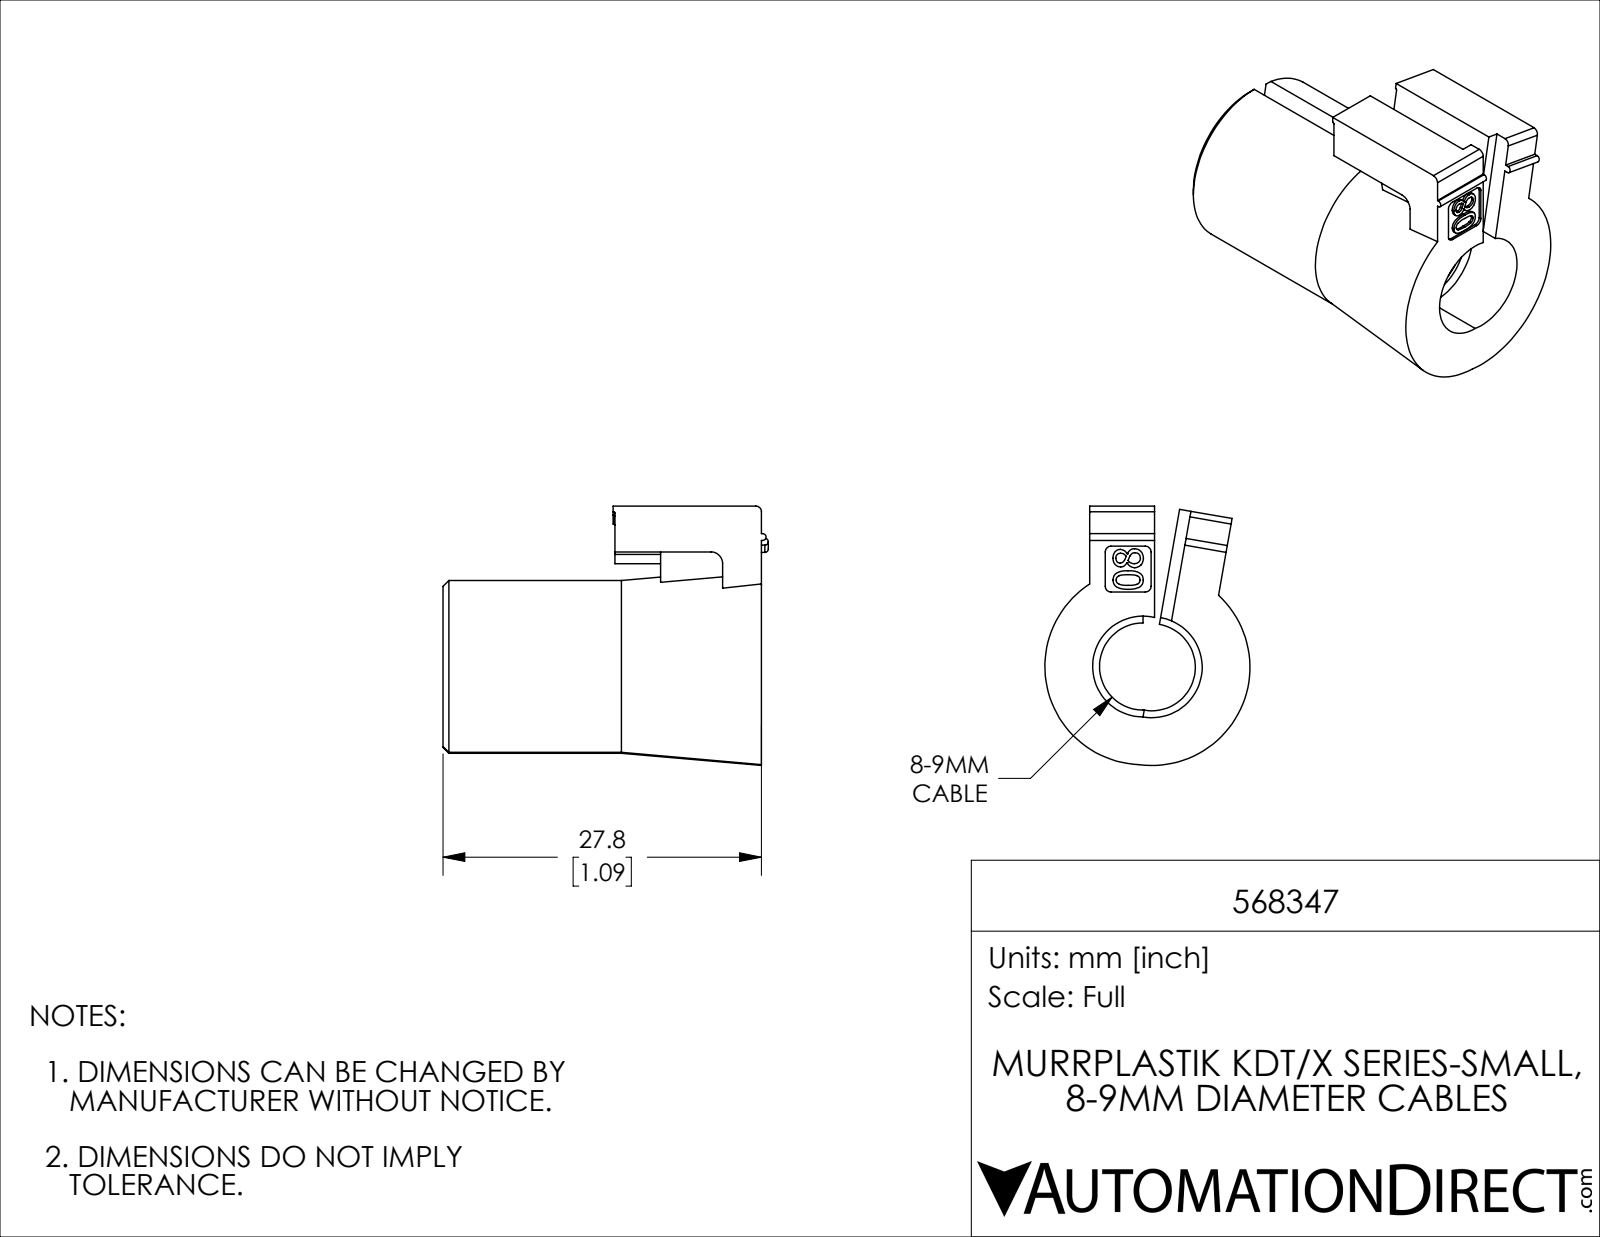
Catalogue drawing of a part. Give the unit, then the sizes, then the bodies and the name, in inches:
Units: inches
Overall size (bounding box): 1.118 × 0.891 × 0.705
Partial cylindrical surfaces — rounded edges, fillets, slot ends (radius × count): R0.02 ×6, R0.004 ×2, R0.012 ×2, R0.039 ×2, R0.15 ×2, R0.173 ×2, R0.295 ×2
Main face-to-face distances: 1.094, 0.157, 0.183, 0.183, 0.504, 0.591, 0.059, 0.445, 1.035, 0.039
Volume: 0.252 in³ · Surface area: 4.839 in²
Bodies: 1 solid, 124 faces (56 planar, 24 cylindrical, 44 other)
Part name (STEP PRODUCT): 568347
STEP written by: SolidWorks 2019 (CONFIG_CONTROL_DESIGN)
